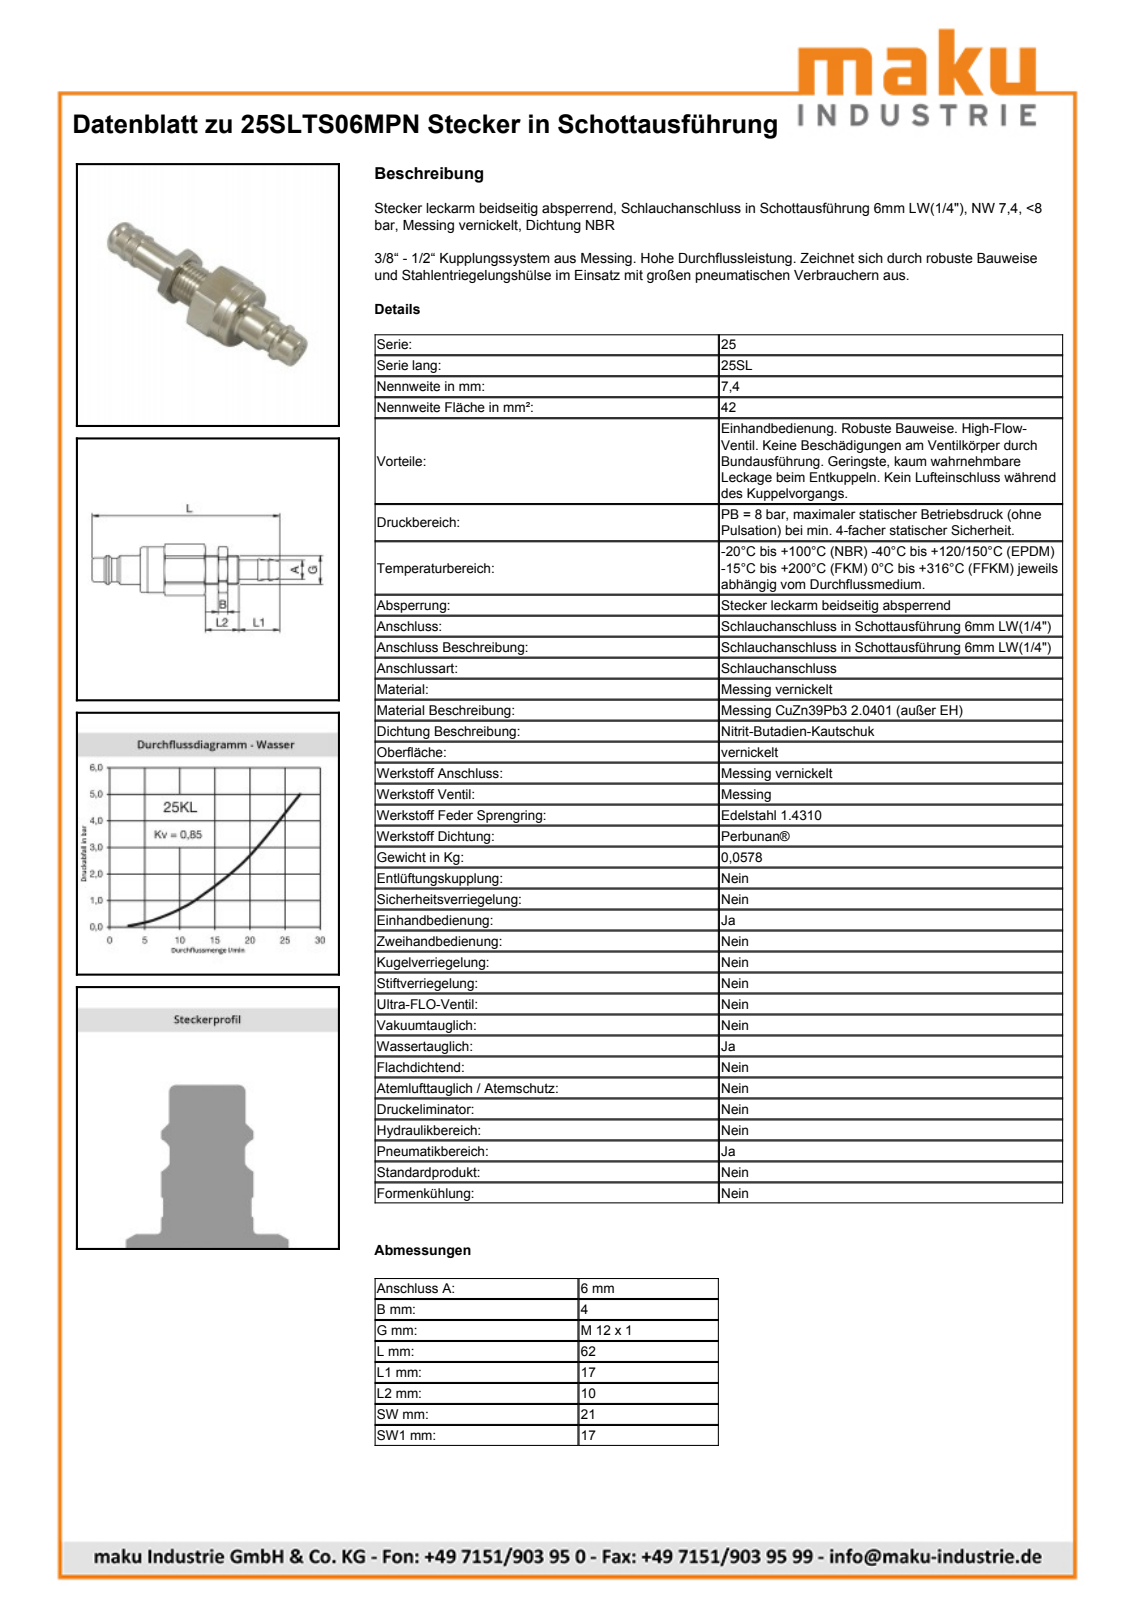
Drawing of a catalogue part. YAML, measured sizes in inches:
part_name: "D110570"
step_written_by: "Autodesk Inventor 2013 (AUTOMOTIVE_DESIGN)"
units: inches
bodies: {solids: 1, faces: 94, planar: 26, cylindrical: 25, other: 43}
overall_size: [2.441, 0.923, 0.894]
volume: 0.573
surface_area: 6.324
round_holes:
  - {diameter: 0.667, count: 1}
round_bosses_or_shafts:
  - {diameter: 0.827, count: 1}
  - {diameter: 0.65, count: 1}
  - {diameter: 0.587, count: 1}
  - {diameter: 0.472, count: 1}
  - {diameter: 0.417, count: 1}
  - {diameter: 0.394, count: 1}
  - {diameter: 0.384, count: 1}
  - {diameter: 0.238, count: 1}
partial_cylinders:
  - {radius: 0.377, count: 1}
  - {radius: 0.467, count: 1}
face_to_face_distances: [0.827, 0.591, 0.669, 0.835, 0.244, 0.677, 0.087, 0.157, 0.394, 0.295]
